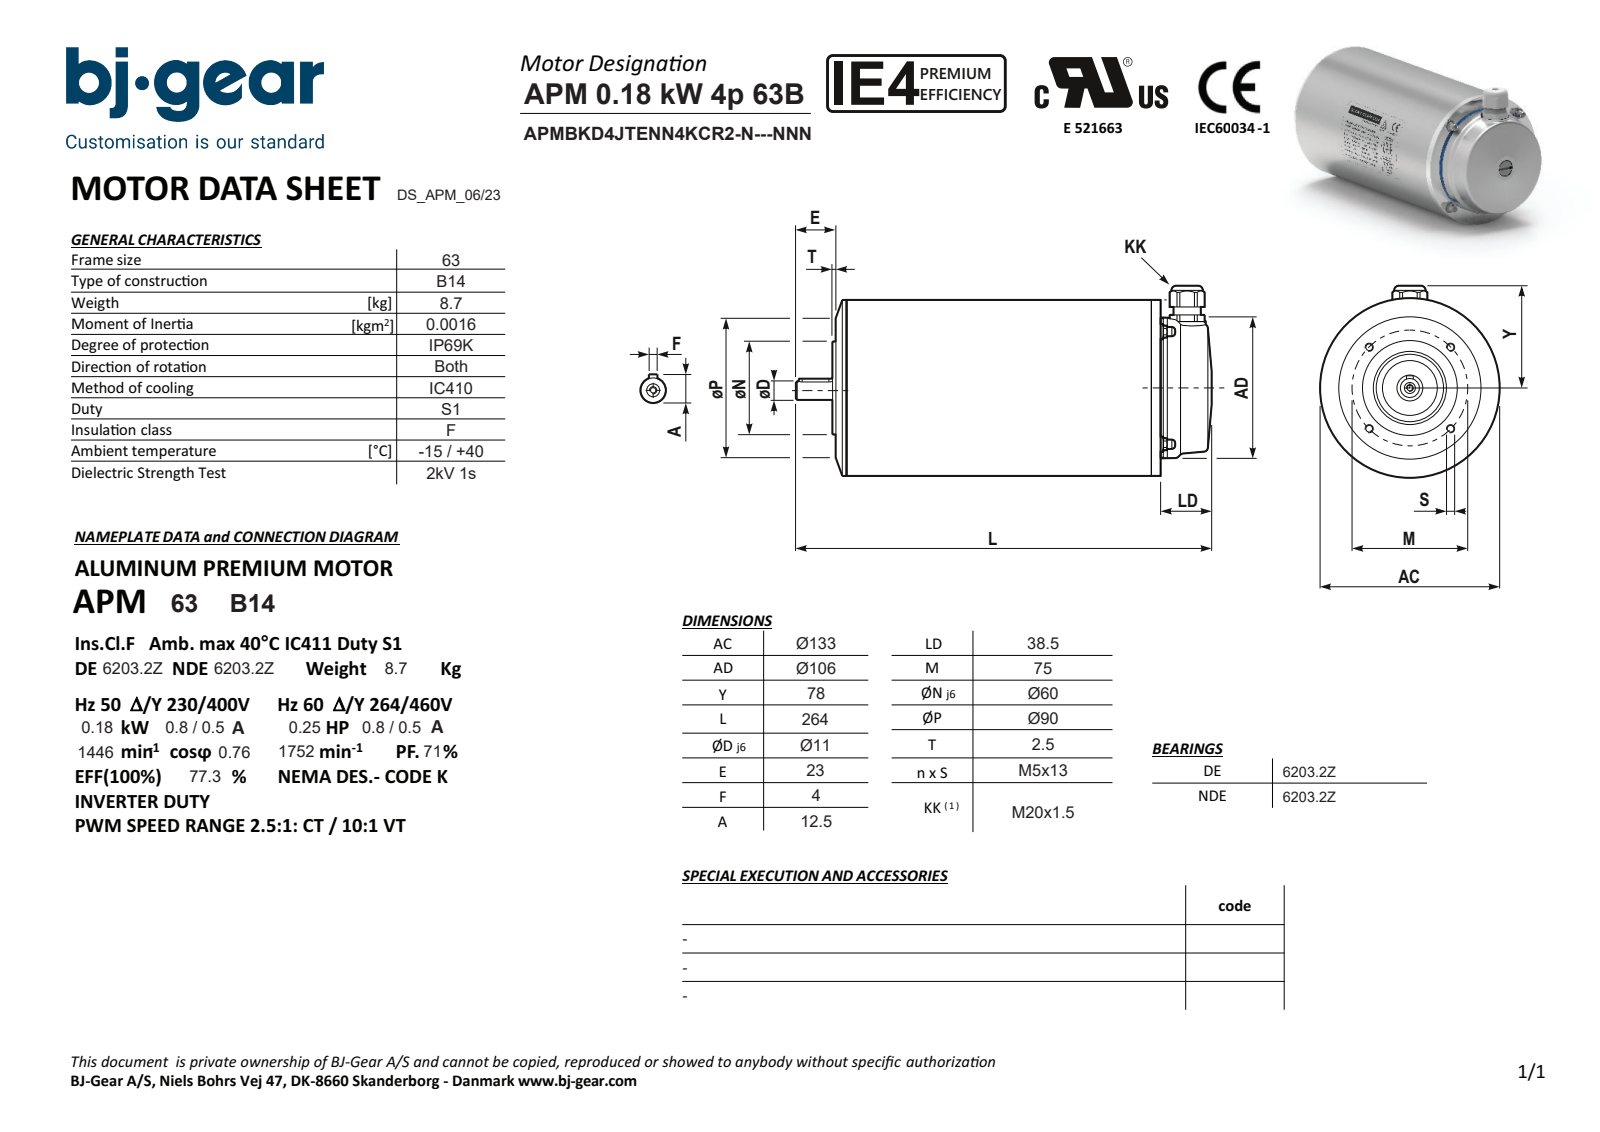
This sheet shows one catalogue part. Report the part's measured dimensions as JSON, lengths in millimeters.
{"part_name": "APMBKD4JTENN4KCR2-N---NNN", "step_written_by": "Solid Edge (AUTOMOTIVE_DESIGN)", "units": "millimeters", "bodies": {"solids": 1, "faces": 148, "planar": 67, "cylindrical": 47, "other": 34}, "overall_size": [264, 143.3, 132.6], "volume_mm3": 3075000, "surface_area_mm2": 127234, "round_holes": [[4.13, 4], [3.24, 1], [4.3, 1], [28, 1], [52, 1]], "round_bosses_or_shafts": [[11.5, 4], [7, 4], [132.6, 1], [132.6, 1], [106, 1], [60, 1], [23.7, 1], [20.6, 1]], "partial_cylinders_radius": [[2, 2], [13.2, 1]], "face_to_face_distances": [202.5, 197, 5.5, 8, 2.5, 205, 38.5, 235.5, 241, 243.5], "hole_center_spacings": [37.5, 53.04, 75.01]}
